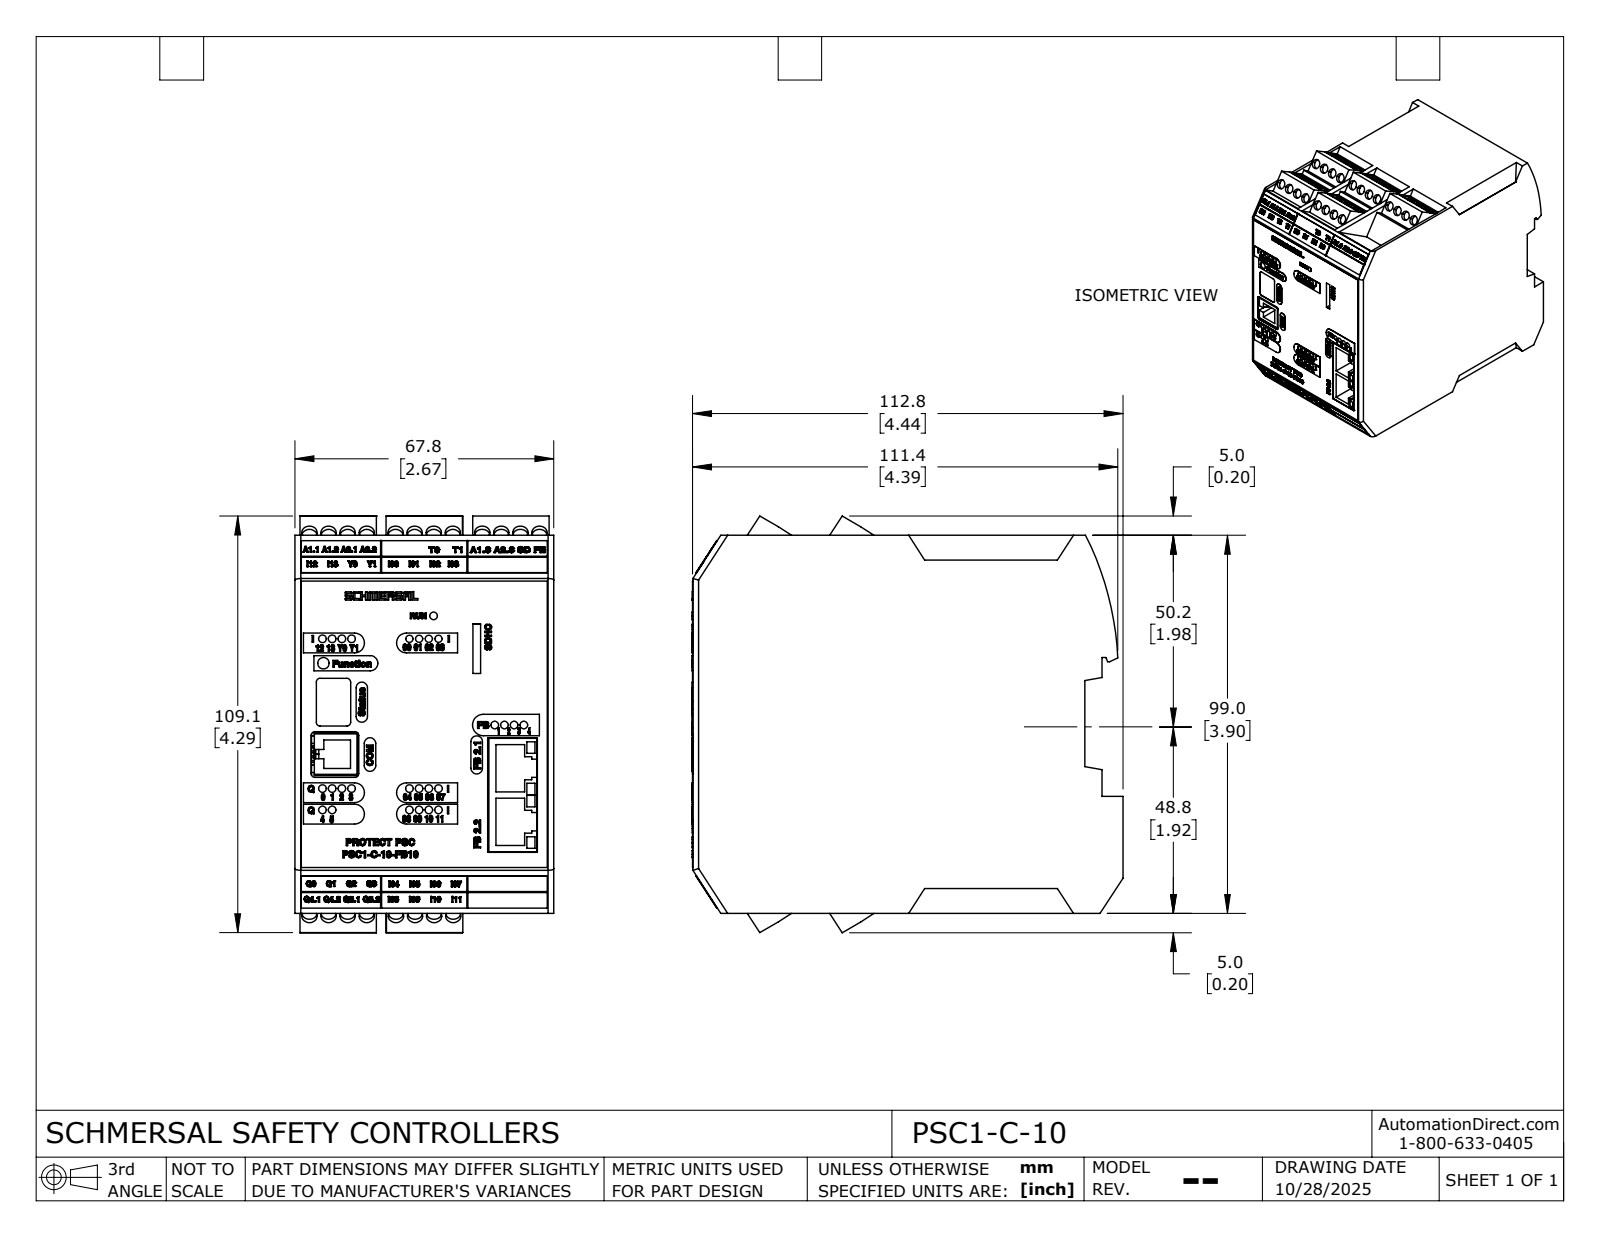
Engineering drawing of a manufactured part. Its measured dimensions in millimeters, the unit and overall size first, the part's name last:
Units: millimetres
Overall size (bounding box): 112.9 × 109.09 × 67.8
Round holes (diameter × count): ⌀4 ×36, ⌀2 ×22, ⌀1.89 ×4, ⌀3 ×1
Round bosses / shafts (diameter × count): ⌀1 ×2, ⌀2 ×1
Partial cylindrical surfaces — rounded edges, fillets, slot ends (radius × count): R1.5 ×14, R1 ×9, R0.3 ×8, R0.4 ×6, R2.6 ×6, R0.45 ×4, R0.7 ×4, R0.2 ×2
Main face-to-face distances: 67.8, 99, 102.75, 10, 22.6, 20.1, 112.75, 18.1, 11.77, 20
Hole centre spacings: 5, 2.54, 10, 11.76, 5.08, 12.78, 39.28, 22.78
Volume: 704 169 mm³ · Surface area: 62 323 mm²
Bodies: 1 solid, 4447 faces (2081 planar, 227 cylindrical, 2139 other)
Part name (STEP PRODUCT): PSC1-C-10
STEP written by: SolidWorks 2024 (AUTOMOTIVE_DESIGN)
